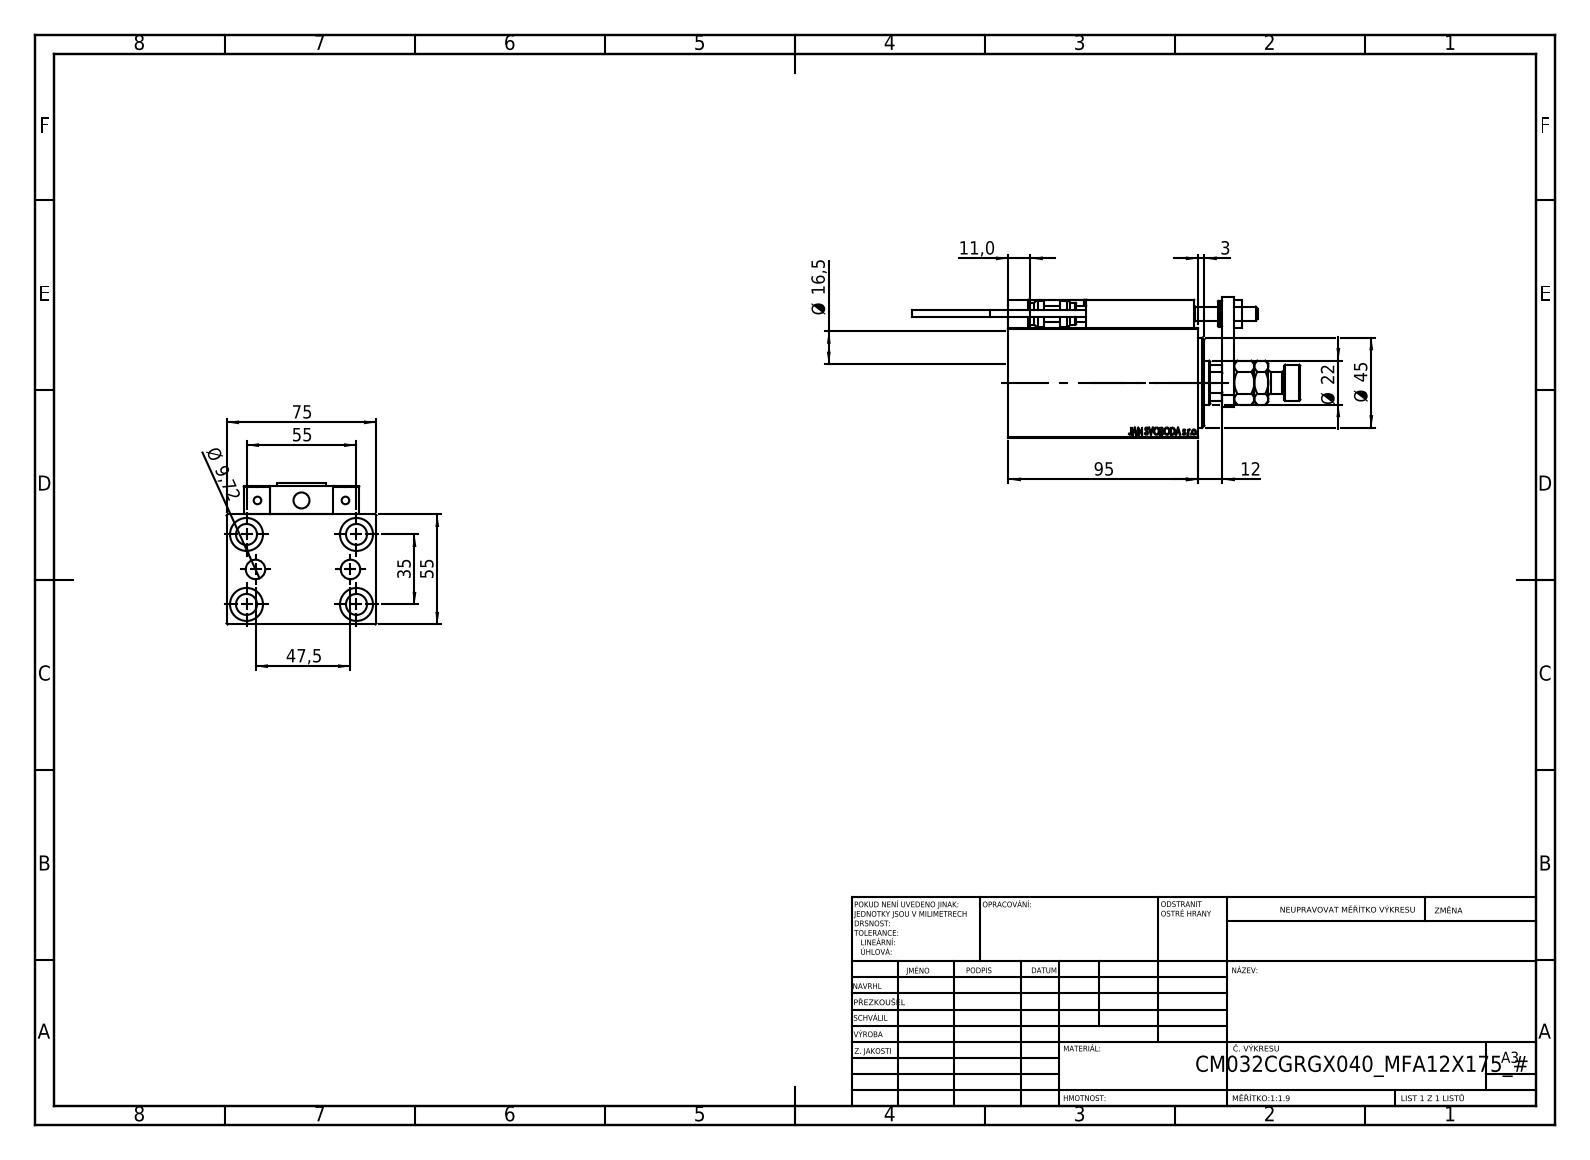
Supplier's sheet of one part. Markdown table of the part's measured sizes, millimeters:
| quantity | value |
| --- | --- |
| part name | V450CM_C_Body; SWITCH_X_FRONT_BACK; KONCOVKA; ALLEN BOLT D8 (+7 more) |
| STEP written by | SolidWorks 2019 (CONFIG_CONTROL_DESIGN) |
| units | millimeters |
| bodies | 24 solids, 1324 faces (574 planar, 184 cylindrical, 566 other) |
| overall size | 194 × 75 × 70.5 |
| volume | 391 664 mm³ |
| surface area | 98 273 mm² |
| round holes (diameter × count) | 8 × 5, 10.5 × 5, 16.5 × 5, 3.2 × 4, 4 × 4, 5 × 2, 9.72 × 2, 7 × 1, 22 × 1, 25.5 × 1, 32 × 1, 34 × 1 |
| round bosses / shafts (diameter × count) | 11 × 2, 5 × 2, 3.8 × 2, 18 × 1, 13 × 1 |
| partial cylindrical surfaces (radius × count) | 0.3 × 30, 3 × 2, 10.5 × 1 |
| main face-to-face distances | 55, 75, 14, 10, 12, 69, 15, 7, 3, 23 |
| hole center spacings | 32.6, 11.37, 17.76, 18.07, 20, 29.59, 29.69, 32.33 |
